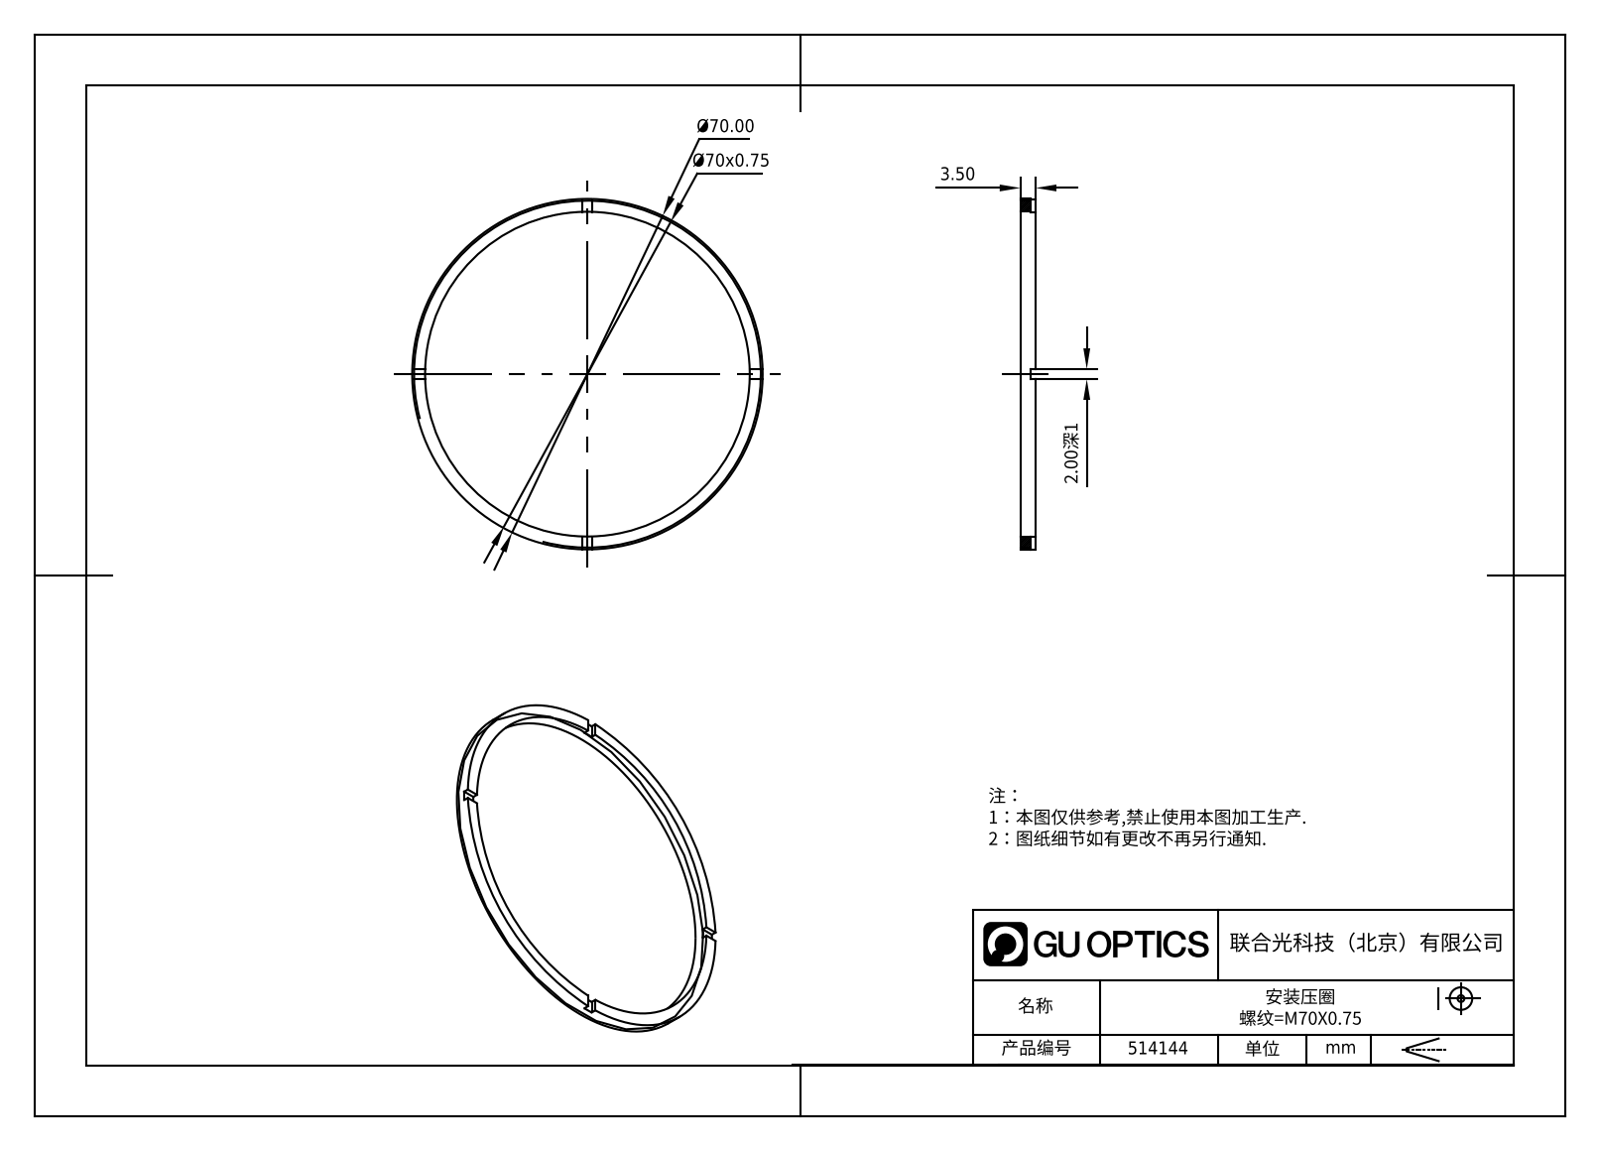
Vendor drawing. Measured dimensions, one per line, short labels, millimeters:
name: 514144
written by: SolidWorks 2020 (CONFIG_CONTROL_DESIGN)
unit: mm
bodies: 1 solid, 21 faces (17 planar, 4 cylindrical, 0 other)
size: 70 × 70 × 3.5
volume: 2 186 mm³; area: 2 744 mm²
holes: 1× ⌀64
bosses: 1× ⌀70
face distances: 3.5, 2.5, 1, 2
